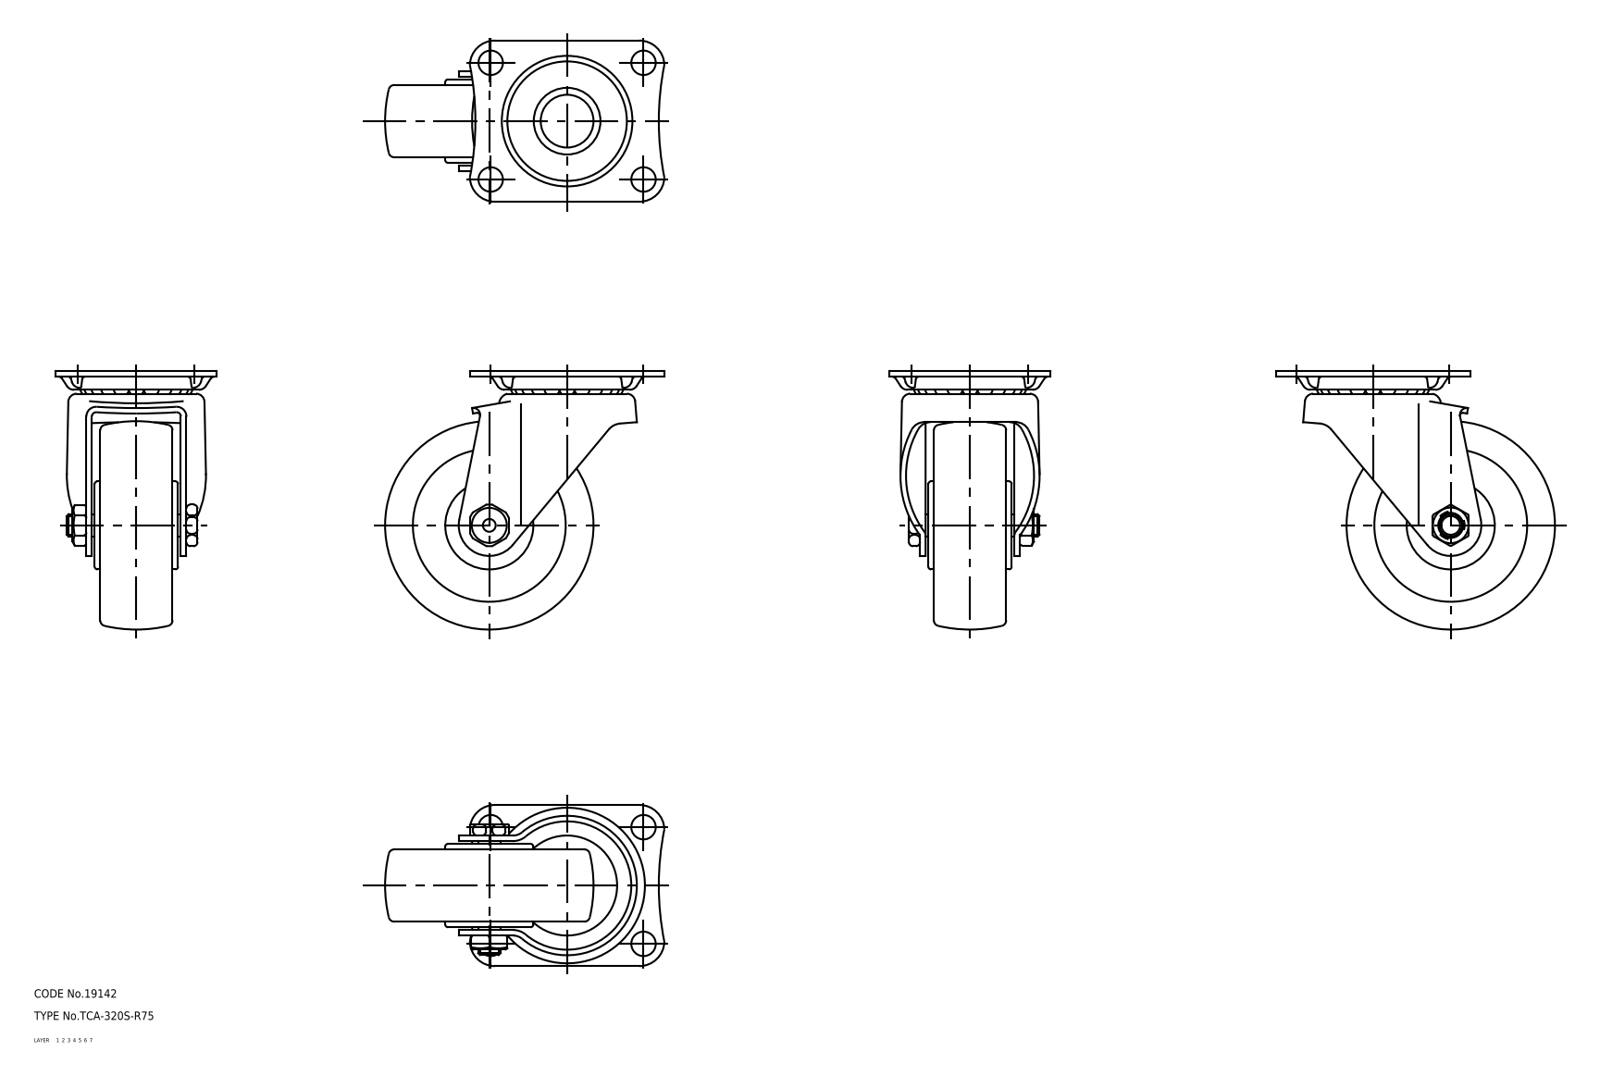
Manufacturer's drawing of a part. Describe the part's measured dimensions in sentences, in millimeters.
The part is named "wheel; mounting plate; main shaft; axle (+1 more)". Its 3-D file was written by "CADfix (AUTOMOTIVE_DESIGN)". It is 5 solids with 329 faces: 0 planar, 0 cylindrical and 329 other. Overall it measures 100.5 by 93 by 58 millimeters. Its volume is 146 426 cubic millimeters and its surface area 44 183 square millimeters.
